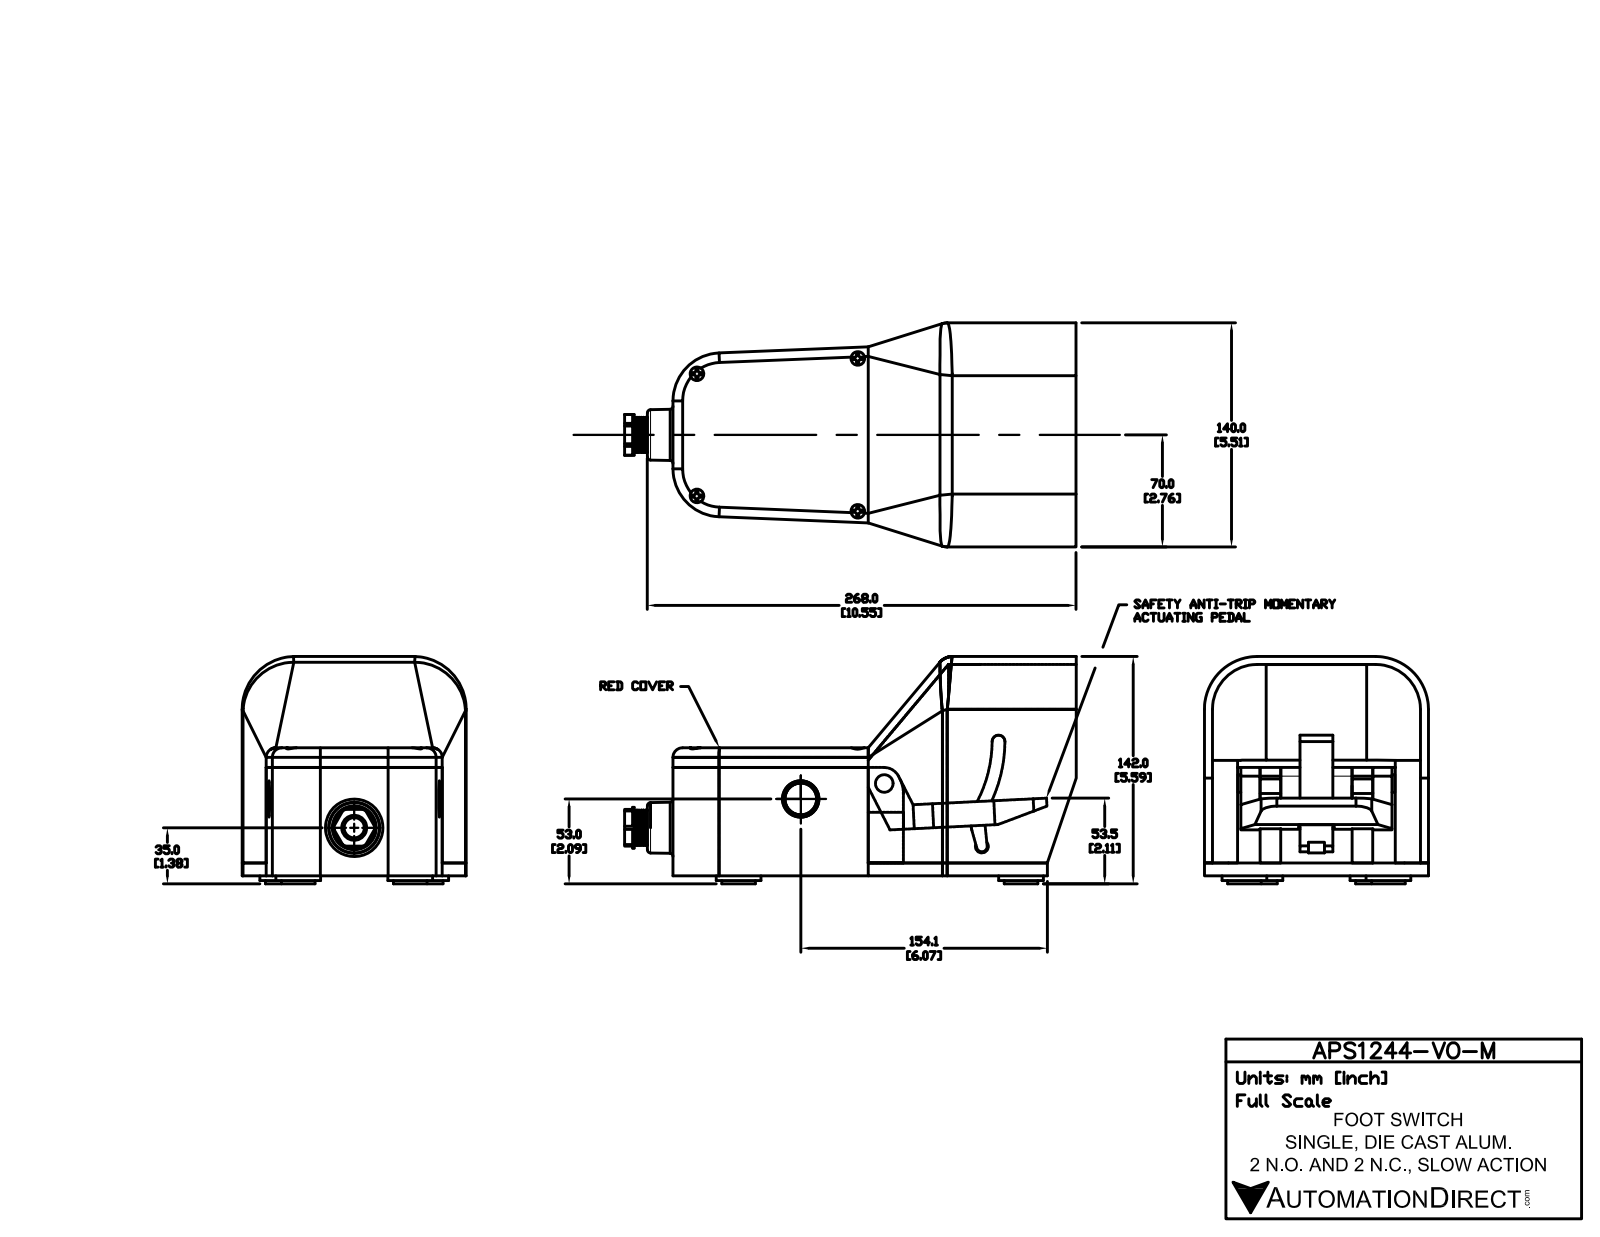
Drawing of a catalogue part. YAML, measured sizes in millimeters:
part_name: "APS1244-V0-M"
step_written_by: "SolidWorks 2015 (AUTOMOTIVE_DESIGN)"
units: millimeters
bodies: {solids: 19, faces: 379, planar: 220, cylindrical: 103, other: 56}
overall_size: [282.25, 142, 140]
volume: 1553000
surface_area: 272464
round_holes:
  - {diameter: 8.5, count: 4}
  - {diameter: 22.75, count: 2}
  - {diameter: 12.65, count: 1}
  - {diameter: 15.6, count: 1}
round_bosses_or_shafts:
  - {diameter: 28, count: 4}
  - {diameter: 21, count: 4}
  - {diameter: 19.87, count: 2}
  - {diameter: 25.5, count: 1}
  - {diameter: 22, count: 1}
  - {diameter: 11, count: 1}
partial_cylinders:
  - {radius: 1, count: 16}
  - {radius: 10, count: 7}
  - {radius: 5.99, count: 3}
  - {radius: 20, count: 2}
  - {radius: 28, count: 2}
  - {radius: 30, count: 2}
  - {radius: 33, count: 2}
  - {radius: 3.35, count: 1}
face_to_face_distances: [5, 135, 8, 59.64, 67.67, 59.67, 67.64, 140, 80, 72]
hole_center_spacings: [101, 132.24, 76.3, 95.5]
